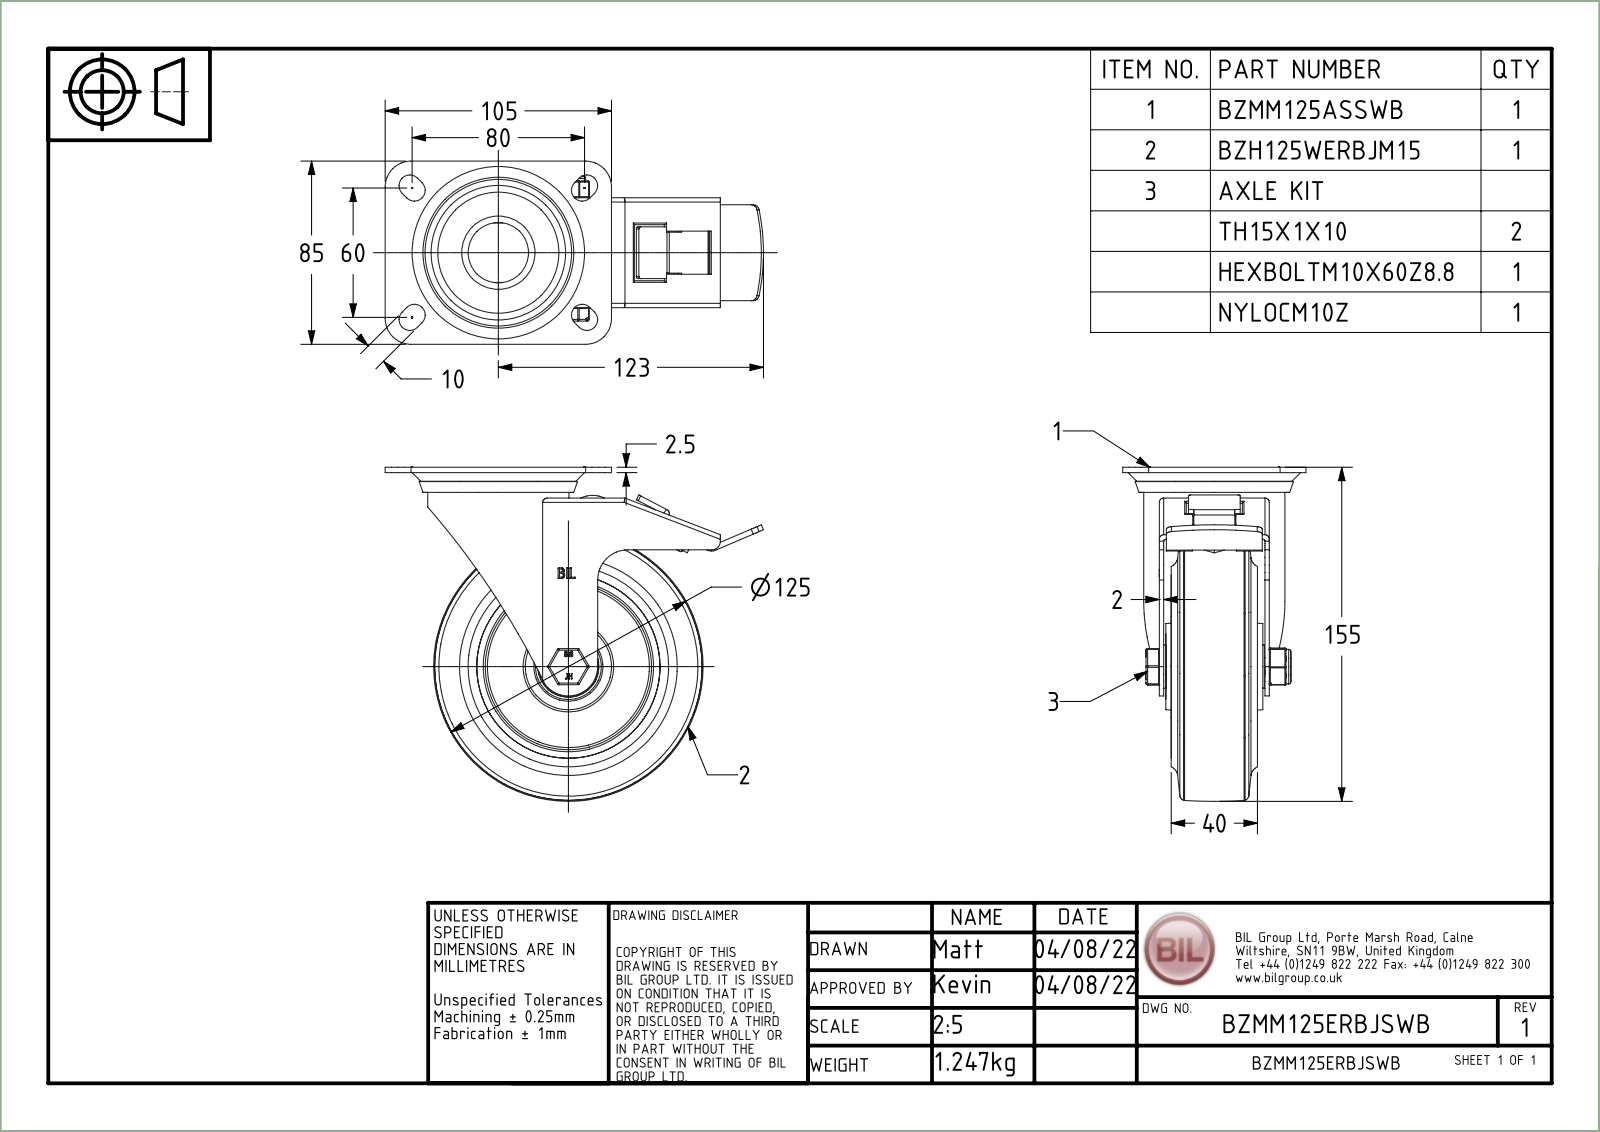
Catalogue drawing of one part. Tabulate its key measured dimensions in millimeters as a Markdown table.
| quantity | value |
| --- | --- |
| part name | BZMM125ASSWB - 47; ZINC PLATED, PRESSED STEEL TOP PLATE; ZINC PLATED, PRESSED STEEL FORKS; BEARING SEAL (+8 more) |
| STEP written by | Spatial InterOp 3D (AUTOMOTIVE_DESIGN) |
| units | millimeters |
| bodies | 44 solids, 1638 faces (634 planar, 450 cylindrical, 554 other) |
| overall size | 175.5 × 155 × 85 |
| volume | 431 676 mm³ |
| surface area | 173 919 mm² |
| round holes (diameter × count) | 6 × 2, 10 × 1, 10.2 × 1, 10.25 × 1, 12 × 1, 15 × 1, 15.5 × 1, 20 × 1, 21 × 1, 27.4 × 1, 28 × 1, 32 × 1 |
| round bosses / shafts (diameter × count) | 65.5 × 1, 34 × 1, 28.4 × 1, 28 × 1, 21.6 × 1, 16 × 1, 14.75 × 1, 8.5 × 1 |
| partial cylindrical surfaces (radius × count) | 0.5 × 18, 0.75 × 16, 1.5 × 12, 5 × 9, 1 × 8, 2 × 6, 3 × 4, 12 × 4 |
| main face-to-face distances | 2, 21.5, 49, 29.5, 27.5, 19.5, 2.5, 5, 3.5, 16 |
| hole center spacings | 43.75 |
